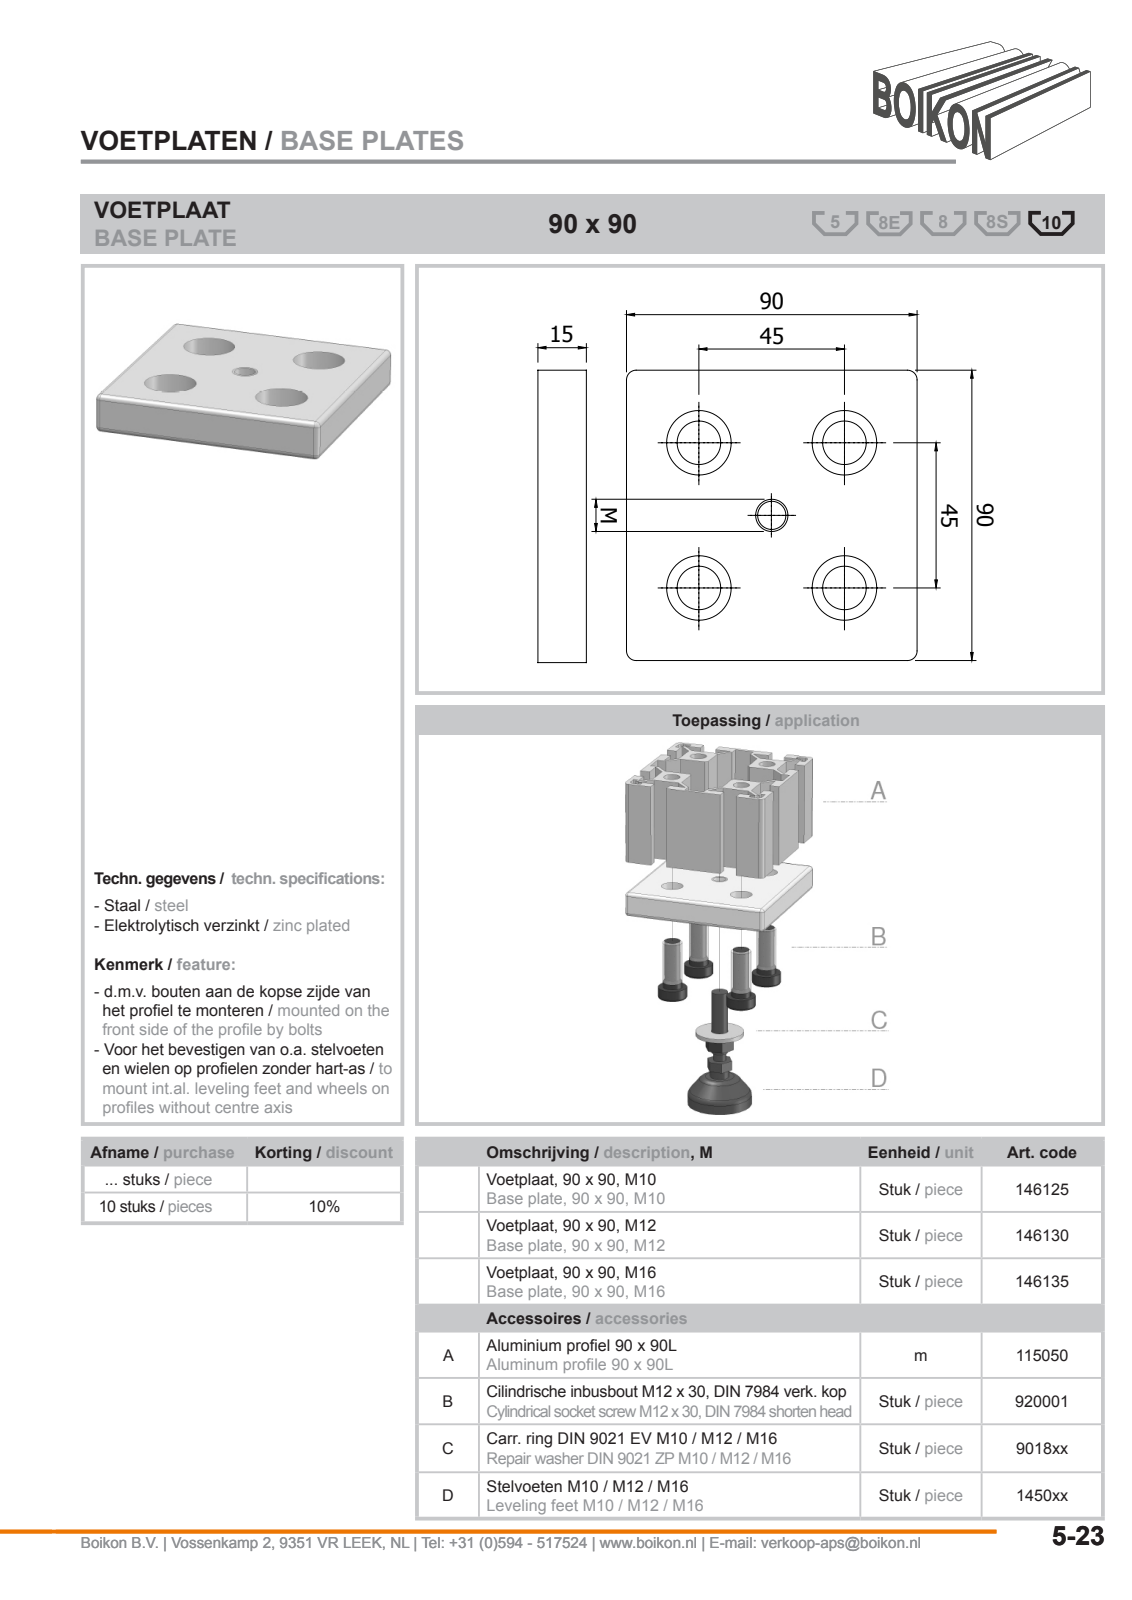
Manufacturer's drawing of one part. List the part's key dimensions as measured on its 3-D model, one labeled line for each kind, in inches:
Part name (STEP PRODUCT): Root; 146130Voetplaat 90x90 M12BOIKON3*; 920001Cil. inb. M12 x 30, DIN 7984 verk. kopBOIKON0
STEP written by: HiCAD 2013 1802.4 Build 509 (AUTOMOTIVE_DESIGN)
Units: inches
Bodies: 5 solids, 107 faces (74 planar, 21 cylindrical, 12 other)
Overall size (bounding box): 3.543 × 3.543 × 1.535
Volume: 7.361 in³ · Surface area: 49.41 in²
Round holes (diameter × count): ⌀0.531 ×4, ⌀0.787 ×4, ⌀0.472 ×1
Round bosses / shafts (diameter × count): ⌀0.709 ×4, ⌀0.472 ×4, ⌀0.388 ×4
Main face-to-face distances: 0.591, 3.543, 0.236, 0.354, 0.079, 0.276, 0.512, 1.457, 0.945, 1.181
Hole centre spacings: 1.253, 1.772, 2.506
